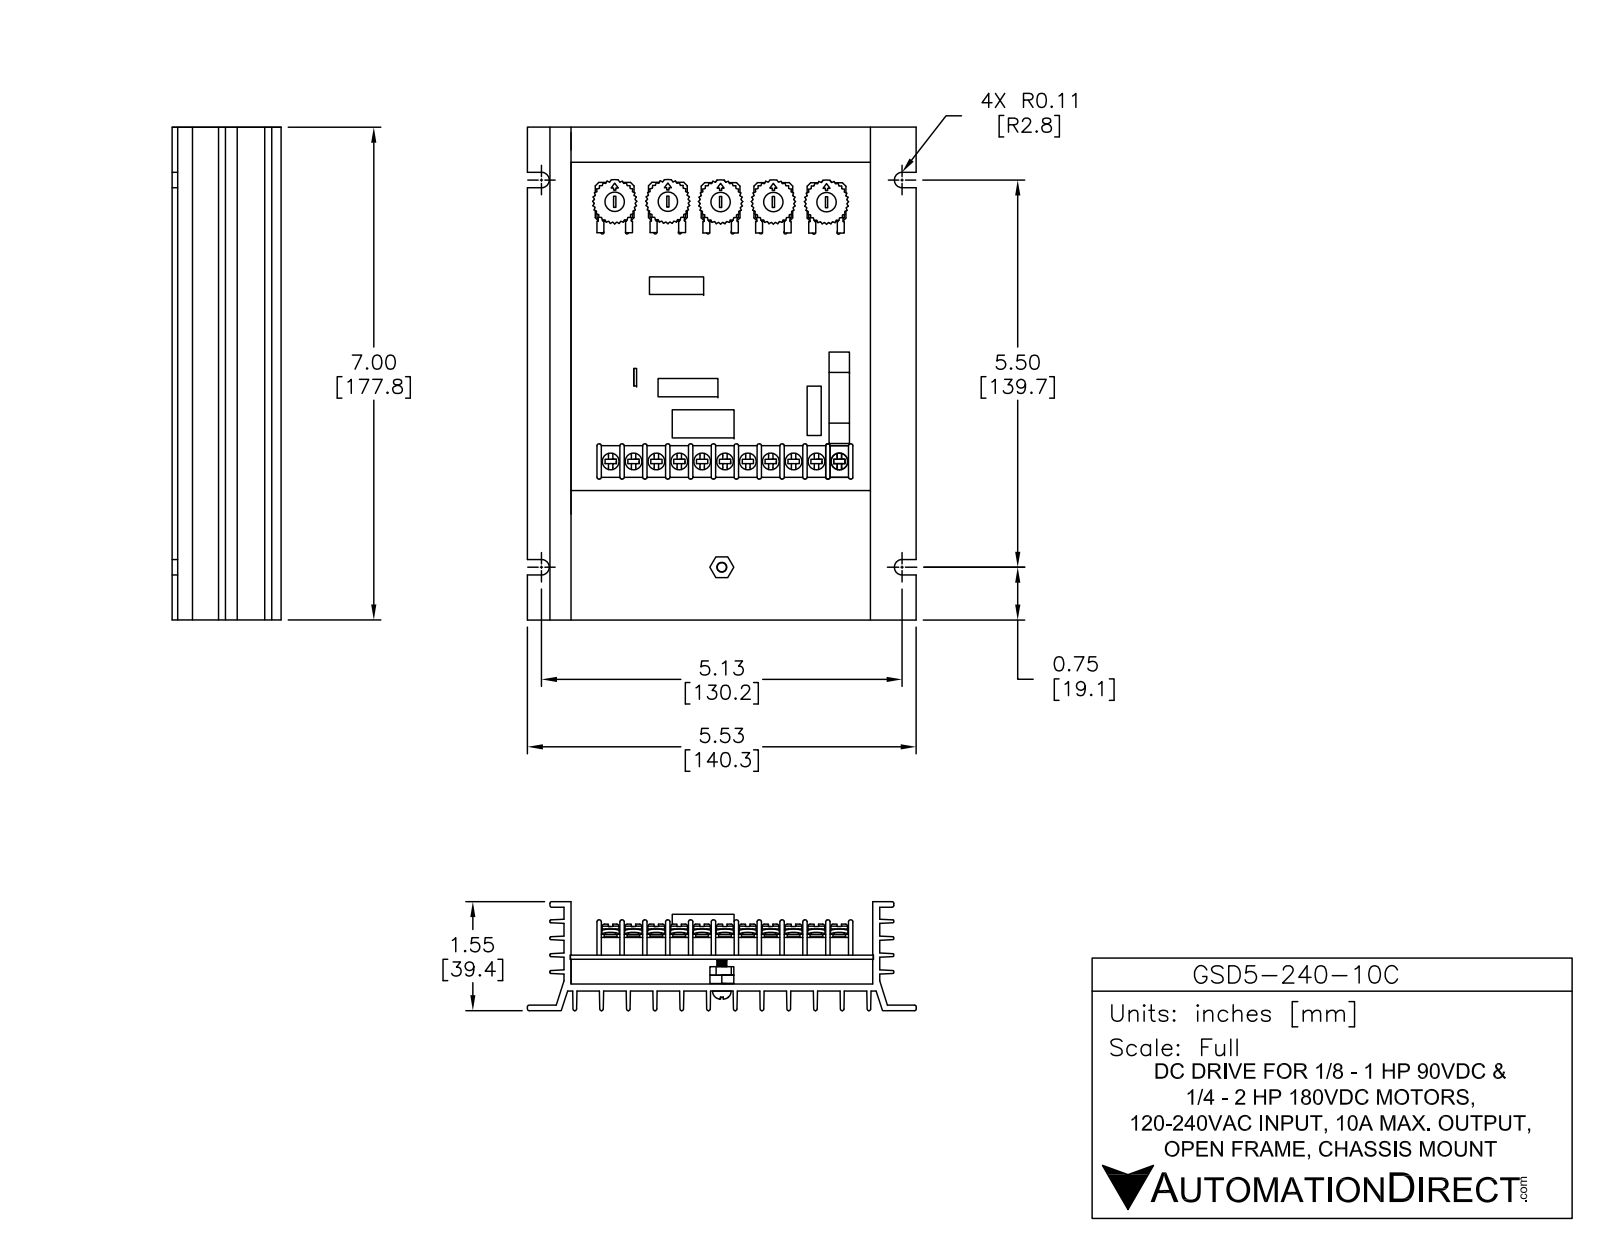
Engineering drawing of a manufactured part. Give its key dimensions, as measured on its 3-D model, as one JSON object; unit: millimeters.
{"part_name": "PC250G; T-BLK_11POS_8.26S-92.5L-12.7W-12.7H; TH_POT_14MMSQ_TW; BMEX250 (+2 more)", "step_written_by": "SolidWorks 2014 (AUTOMOTIVE_DESIGN)", "units": "millimeters", "bodies": {"solids": 8, "faces": 1850, "planar": 1379, "cylindrical": 390, "other": 81}, "overall_size": [177.8, 140.4, 39.4], "volume_mm3": 162900, "surface_area_mm2": 166100, "round_holes": [[7, 5], [2.9, 4], [2.6, 3], [1.5, 1]], "round_bosses_or_shafts": [[6, 11], [3.6, 11], [1.7, 7], [4.4, 5], [1.7, 4]], "partial_cylinders_radius": [[0.6, 74], [0.5, 12], [9.9, 11], [12.3, 11], [0.5, 8], [8, 5], [1, 4], [2.8, 4]], "face_to_face_distances": [18.3, 2.5, 36.6, 9.1, 11.6, 1.6, 10.1, 7.5, 9.1, 54.8], "hole_center_spacings": [21.1, 42.2, 63.4, 92.7, 116.9, 131, 149.2, 1.1]}
